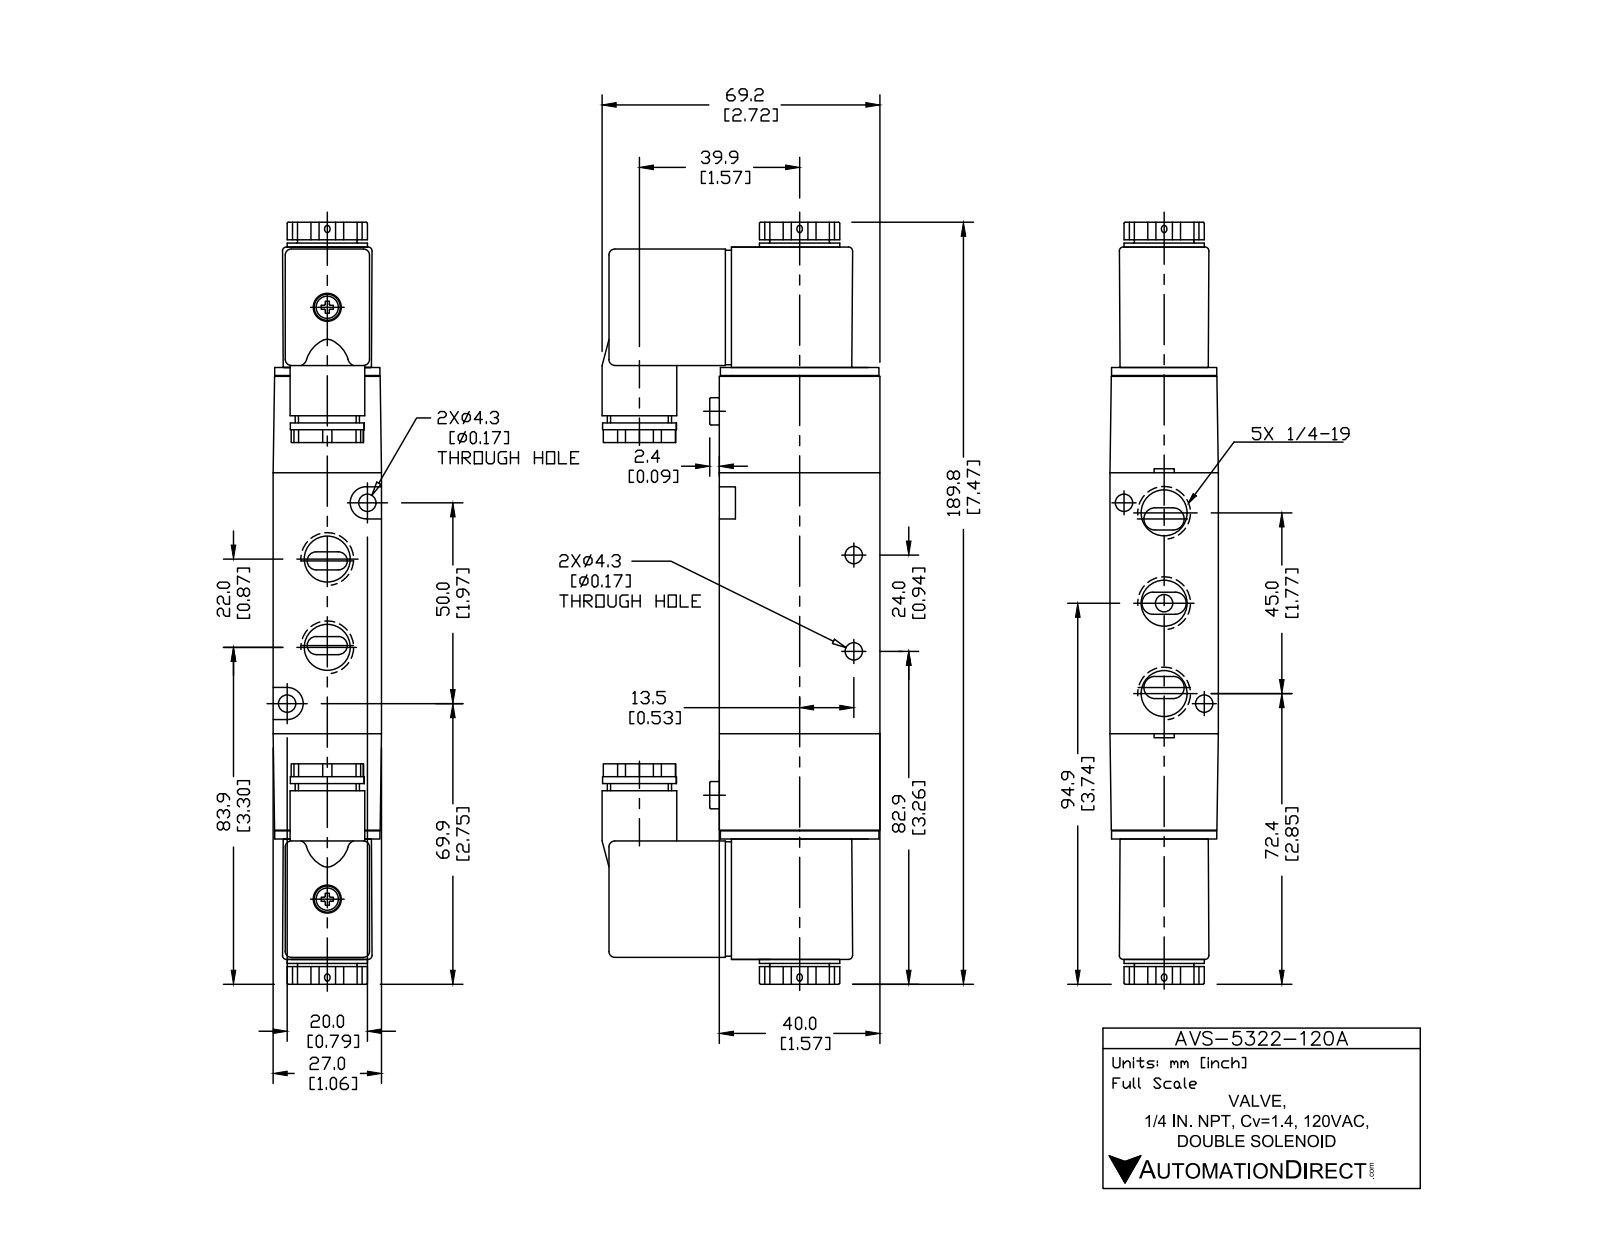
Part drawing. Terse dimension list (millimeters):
name: AVS-5322-120A
written by: SolidWorks 2015 (CONFIG_CONTROL_DESIGN)
unit: mm
bodies: 5 solids, 272 faces (127 planar, 111 cylindrical, 34 other)
size: 189.8 × 69.2 × 27
volume: 204 171 mm³; area: 43 007 mm²
holes: 5× ⌀11.13, 4× ⌀4.3, 1× ⌀9.3
bosses: 2× ⌀6.7, 1× ⌀20, 1× ⌀18.6, 1× ⌀18.4, 1× ⌀16, 1× ⌀14.8
rounds: 18× R1.5, 10× R1, 10× R1.54, 8× R0.5, 2× R3
face distances: 27, 3, 24, 40, 65, 23.06, 21, 29.5, 0.5, 147.4
hole spacings: 10.31, 11, 11.5, 17.2, 22.5, 26.93, 33.5, 37.36
